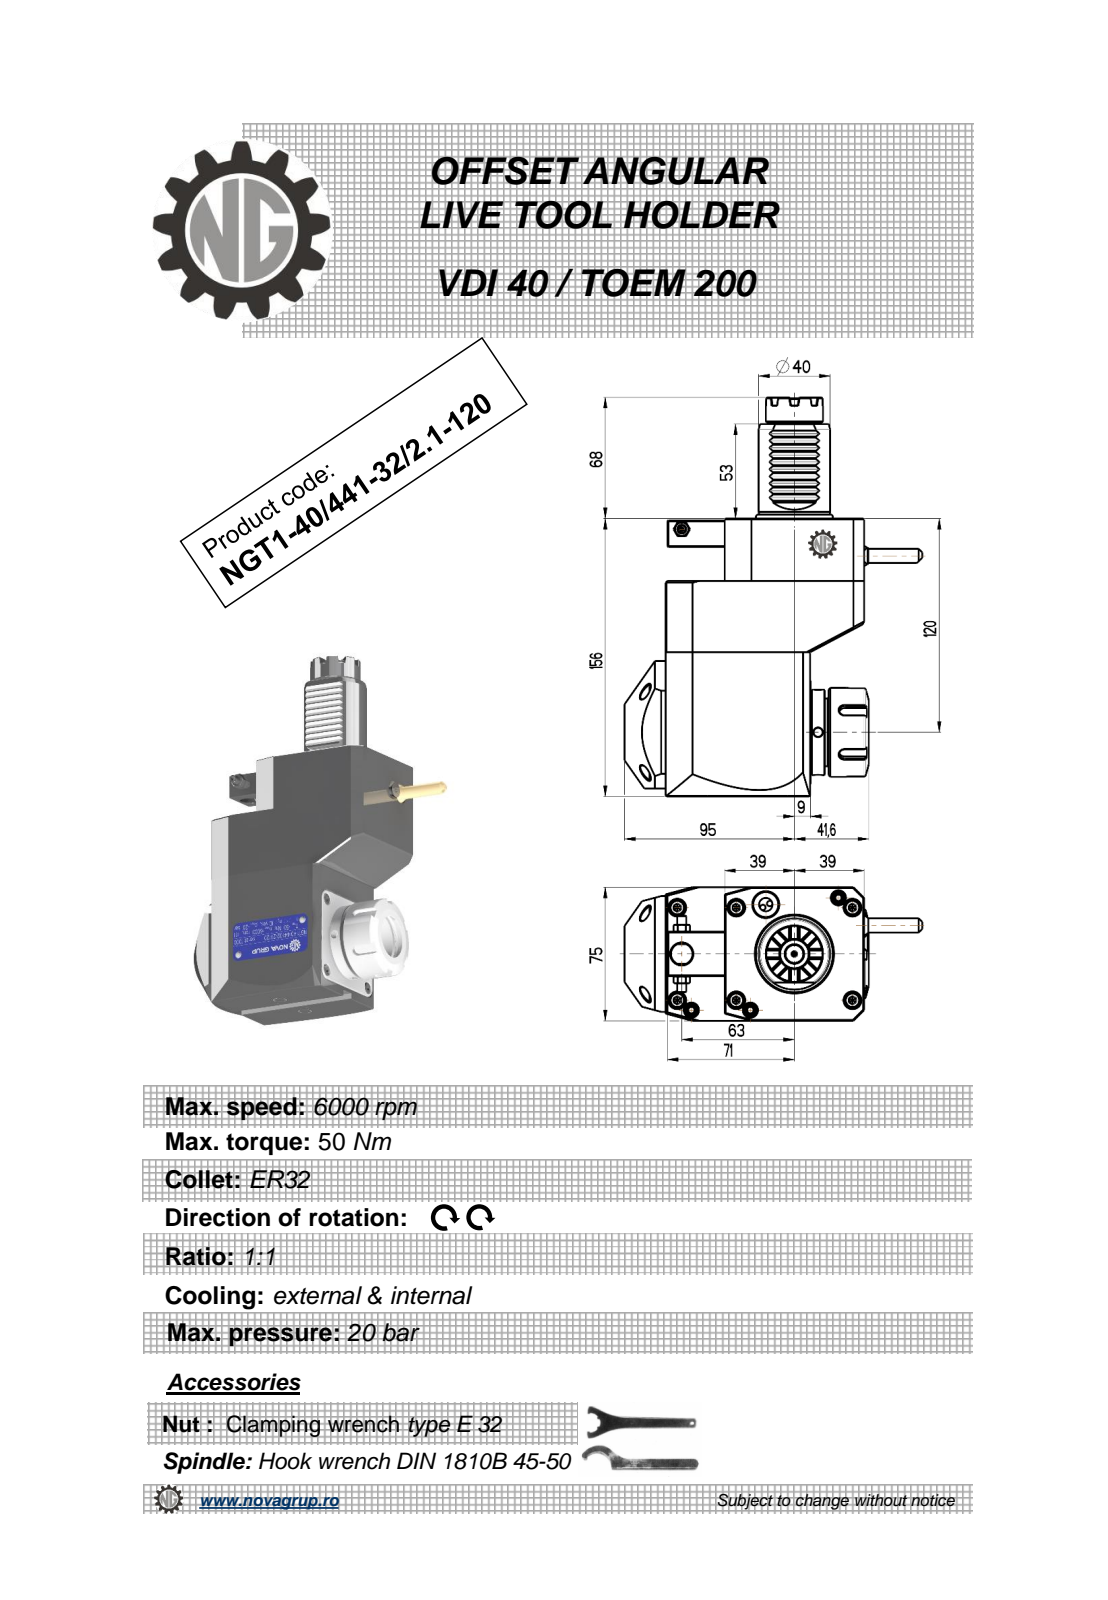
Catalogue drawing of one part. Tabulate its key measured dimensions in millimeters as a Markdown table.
| quantity | value |
| --- | --- |
| part name | NGT1_40_441_32_2_1_120 |
| STEP written by | PRO/ENGINEER BY PARAMETRIC TECHNOLOGY CORPORATION, 2010280 (CONFIG_CONTROL_DESIGN) |
| units | millimeters |
| bodies | 1 solid, 500 faces (239 planar, 94 cylindrical, 167 other) |
| overall size | 224 × 166.5 × 76.6 |
| volume | 1 201 000 mm³ |
| surface area | 89 432 mm² |
| round holes (diameter × count) | 5 × 3, 3 × 1, 9.5 × 1, 12 × 1, 27 × 1 |
| round bosses / shafts (diameter × count) | 50 × 1, 48 × 1, 41 × 1, 40 × 1, 32 × 1, 17 × 1, 10 × 1, 8.96 × 1 |
| partial cylindrical surfaces (radius × count) | 0.26 × 12, 0.3 × 10, 0.2 × 6, 3 × 5, 0.5 × 1, 8.6 × 1, 40 × 1 |
| main face-to-face distances | 75, 156, 111, 35, 121, 81, 30, 33, 78, 48 |
| hole center spacings | 20.93, 76.25, 100.28, 112.5 |
